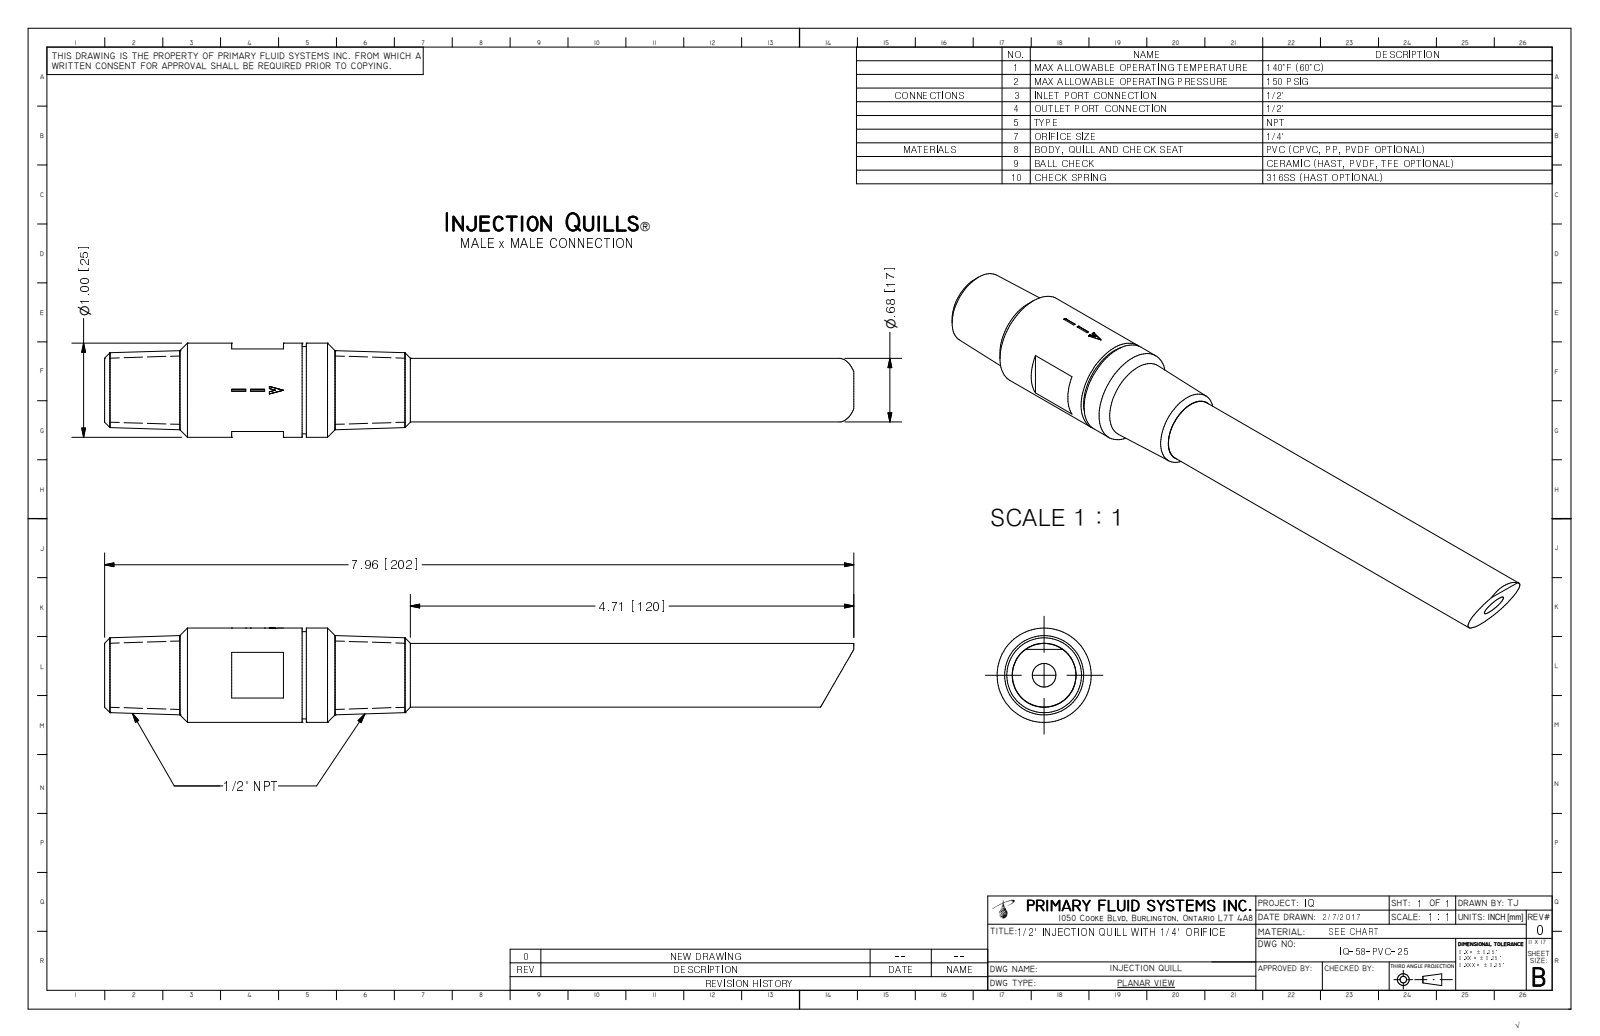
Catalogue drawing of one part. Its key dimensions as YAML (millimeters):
part_name: "IQ-58-PVC-25_R0"
step_written_by: "Autodesk Inventor 2009 (AUTOMOTIVE_DESIGN)"
units: millimeters
bodies: {solids: 1, faces: 47, planar: 26, cylindrical: 11, other: 10}
overall_size: [202.3, 25.4, 25.4]
volume: 54140
surface_area: 17710
round_holes:
  - {diameter: 6.4, count: 1}
  - {diameter: 11.9, count: 1}
  - {diameter: 14.2, count: 1}
round_bosses_or_shafts:
  - {diameter: 25.4, count: 1}
  - {diameter: 23.5, count: 1}
  - {diameter: 17.1, count: 1}
  - {diameter: 14.2, count: 1}
partial_cylinders:
  - {radius: 12.7, count: 1}
face_to_face_distances: [22.2, 19.1, 34.3, 53.3, 54.5, 35.4, 1.1, 3.8, 38.1, 57.2]
